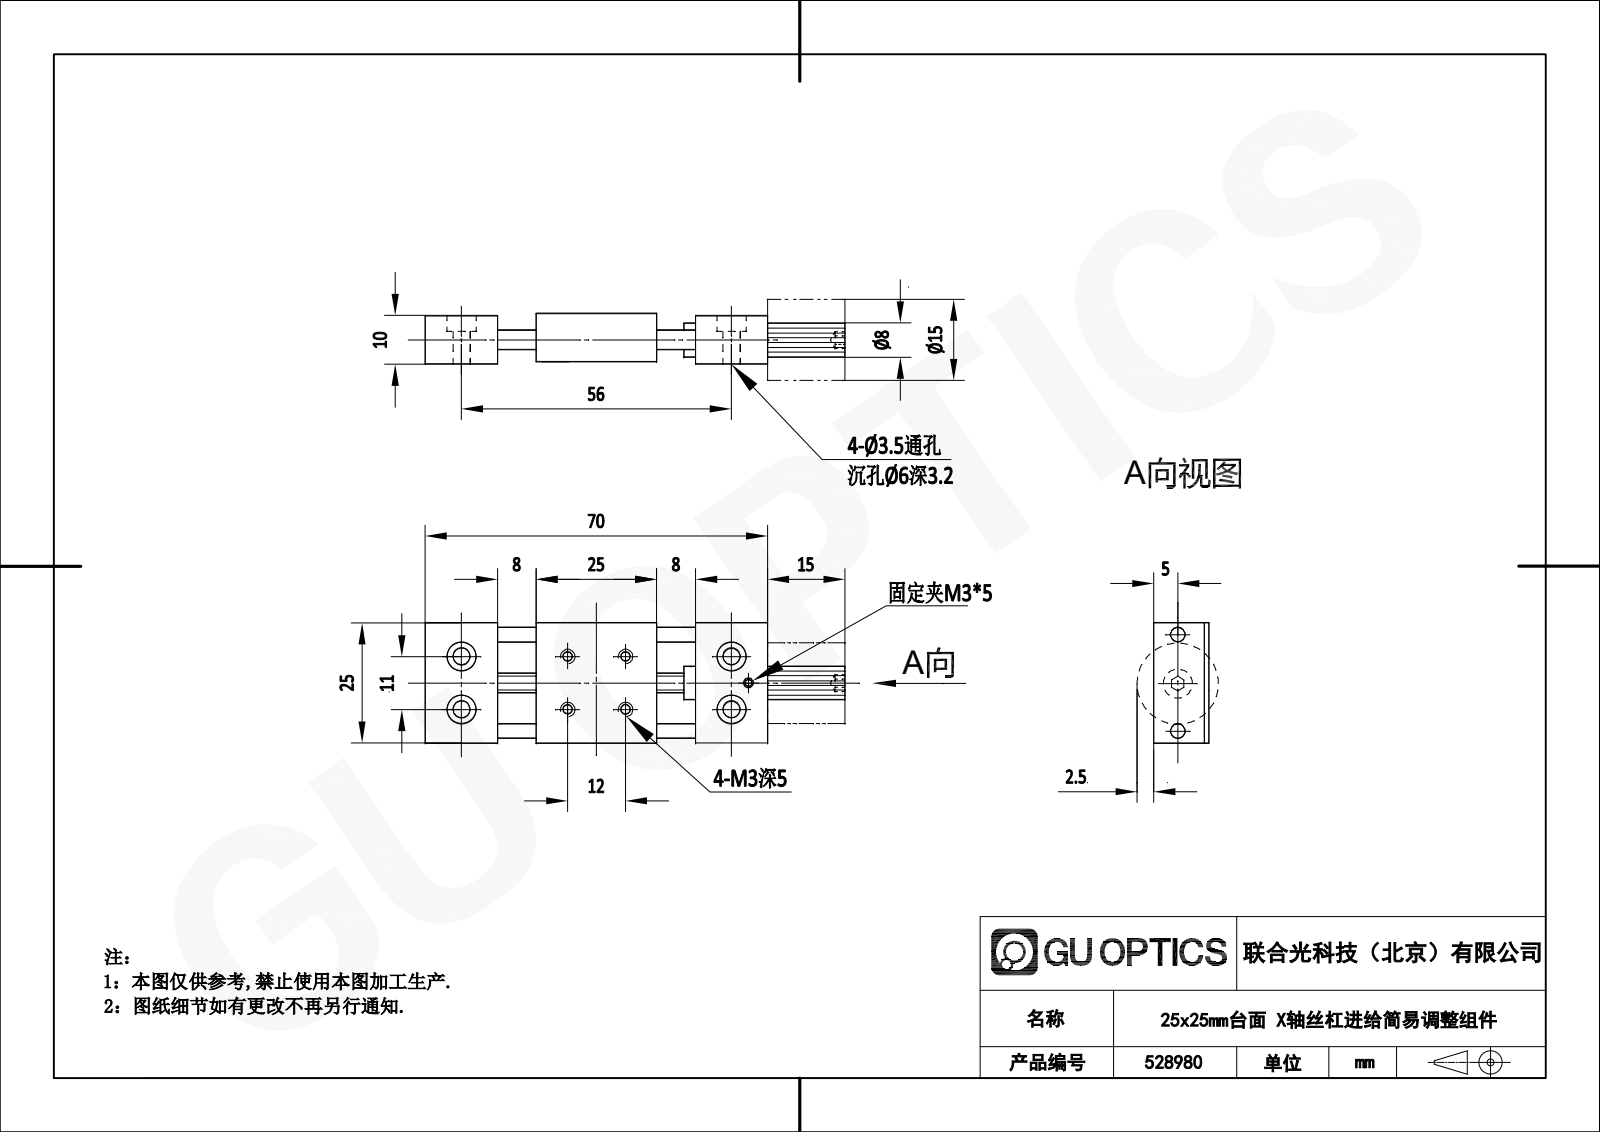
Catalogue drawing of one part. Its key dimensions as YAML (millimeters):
part_name: "528980"
step_written_by: "SolidWorks 2020 (CONFIG_CONTROL_DESIGN)"
units: millimeters
bodies: {solids: 6, faces: 319, planar: 150, cylindrical: 68, other: 101}
overall_size: [86.5, 25, 10.5]
volume: 13435
surface_area: 10377
round_holes:
  - {diameter: 2.46, count: 7}
  - {diameter: 6, count: 5}
  - {diameter: 2.46, count: 4}
  - {diameter: 3.2, count: 4}
  - {diameter: 3, count: 3}
round_bosses_or_shafts:
  - {diameter: 7, count: 1}
  - {diameter: 5.6, count: 1}
  - {diameter: 4, count: 1}
partial_cylinders:
  - {radius: 4, count: 1}
face_to_face_distances: [0.5, 10, 25, 9.5, 10.5, 14.5, 56, 70.5, 41.5, 47.5]
hole_center_spacings: [4.5, 8.14, 10, 11, 15.5, 56, 56.18, 58.11]
